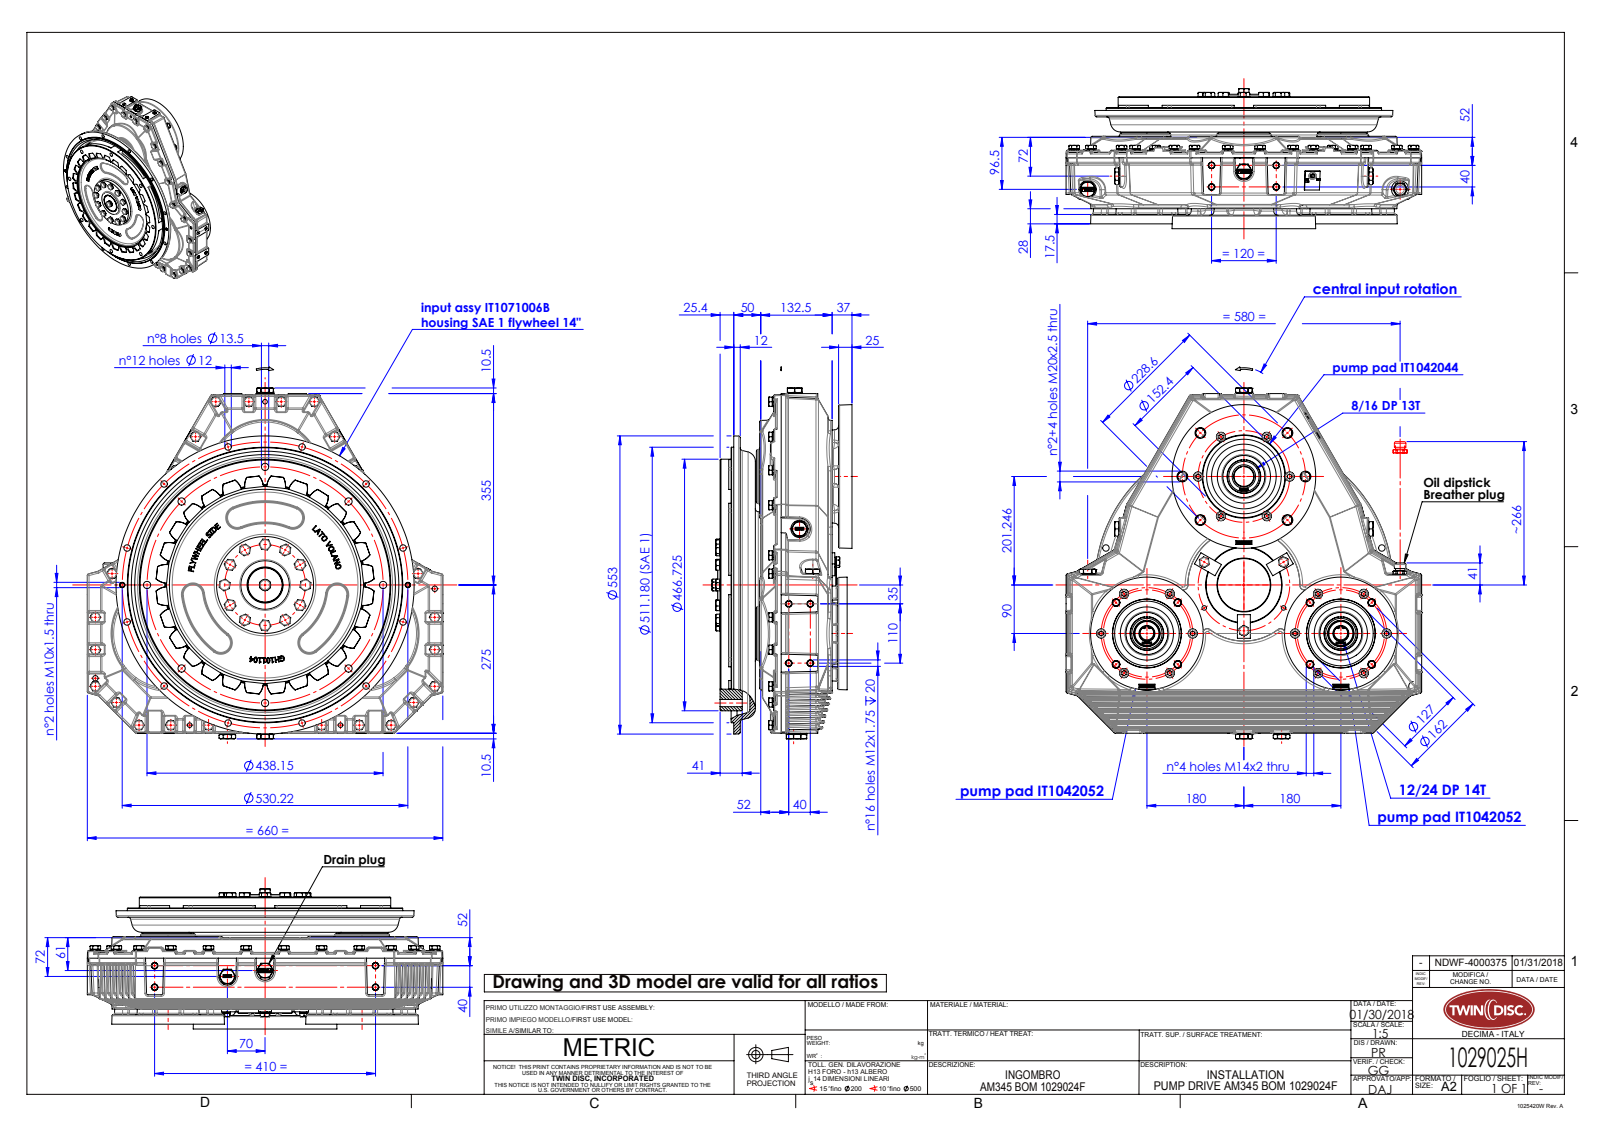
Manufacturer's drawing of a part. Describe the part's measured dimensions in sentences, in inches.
The part is named "IT2021216_rev03-installation; ITam230-002_rev00-installation; ITam230-001_rev01-installation; ITB00610000_rev02-installation (+6 more)". Its 3-D file was written by "SolidWorks 2015 (AUTOMOTIVE_DESIGN)". It is 52 solids with 10213 faces: 4565 planar, 2579 cylindrical and 3069 other. Overall it measures 27.167 by 25.984 by 10.236 inches. Its volume is 669.4 cubic inches and its surface area 5 831 square inches. Round holes: 52 of diameter 0.402, 37 of diameter 0.335, 32 of diameter 0.472, 30 of diameter 0.413, 21 of diameter 0.433, 19 of diameter 0.512, 18 of diameter 0.669, 10 of diameter 0.394, 8 of diameter 0.531, 8 of diameter 0.551, 7 of diameter 0.48, 6 of diameter 0.689. Round bosses or shafts: 53 of diameter 0.394, 33 of diameter 0.713, 33 of diameter 0.638, 19 of diameter 0.709, 19 of diameter 0.472, 18 of diameter 0.63, 12 of diameter 0.945, 7 of diameter 0.831. Partial cylindrical surfaces (rounded edges, fillets, slot ends): 369 of radius 0.118, 126 of radius 0.079, 112 of radius 0.03, 98 of radius 0.197, 58 of radius 0.018, 56 of radius 1.339, 56 of radius 1.346, 44 of radius 0.059. The main face-to-face distances are 0.394, 6.004, 5.61, 2.004, 1.61, 1.102, 0.709, 1.457, 5.217, 6.713. The hole center spacings are 2.26, 4.724, 5.456, 1.575, 8.183, 2.022, 2.622, 3.363.
